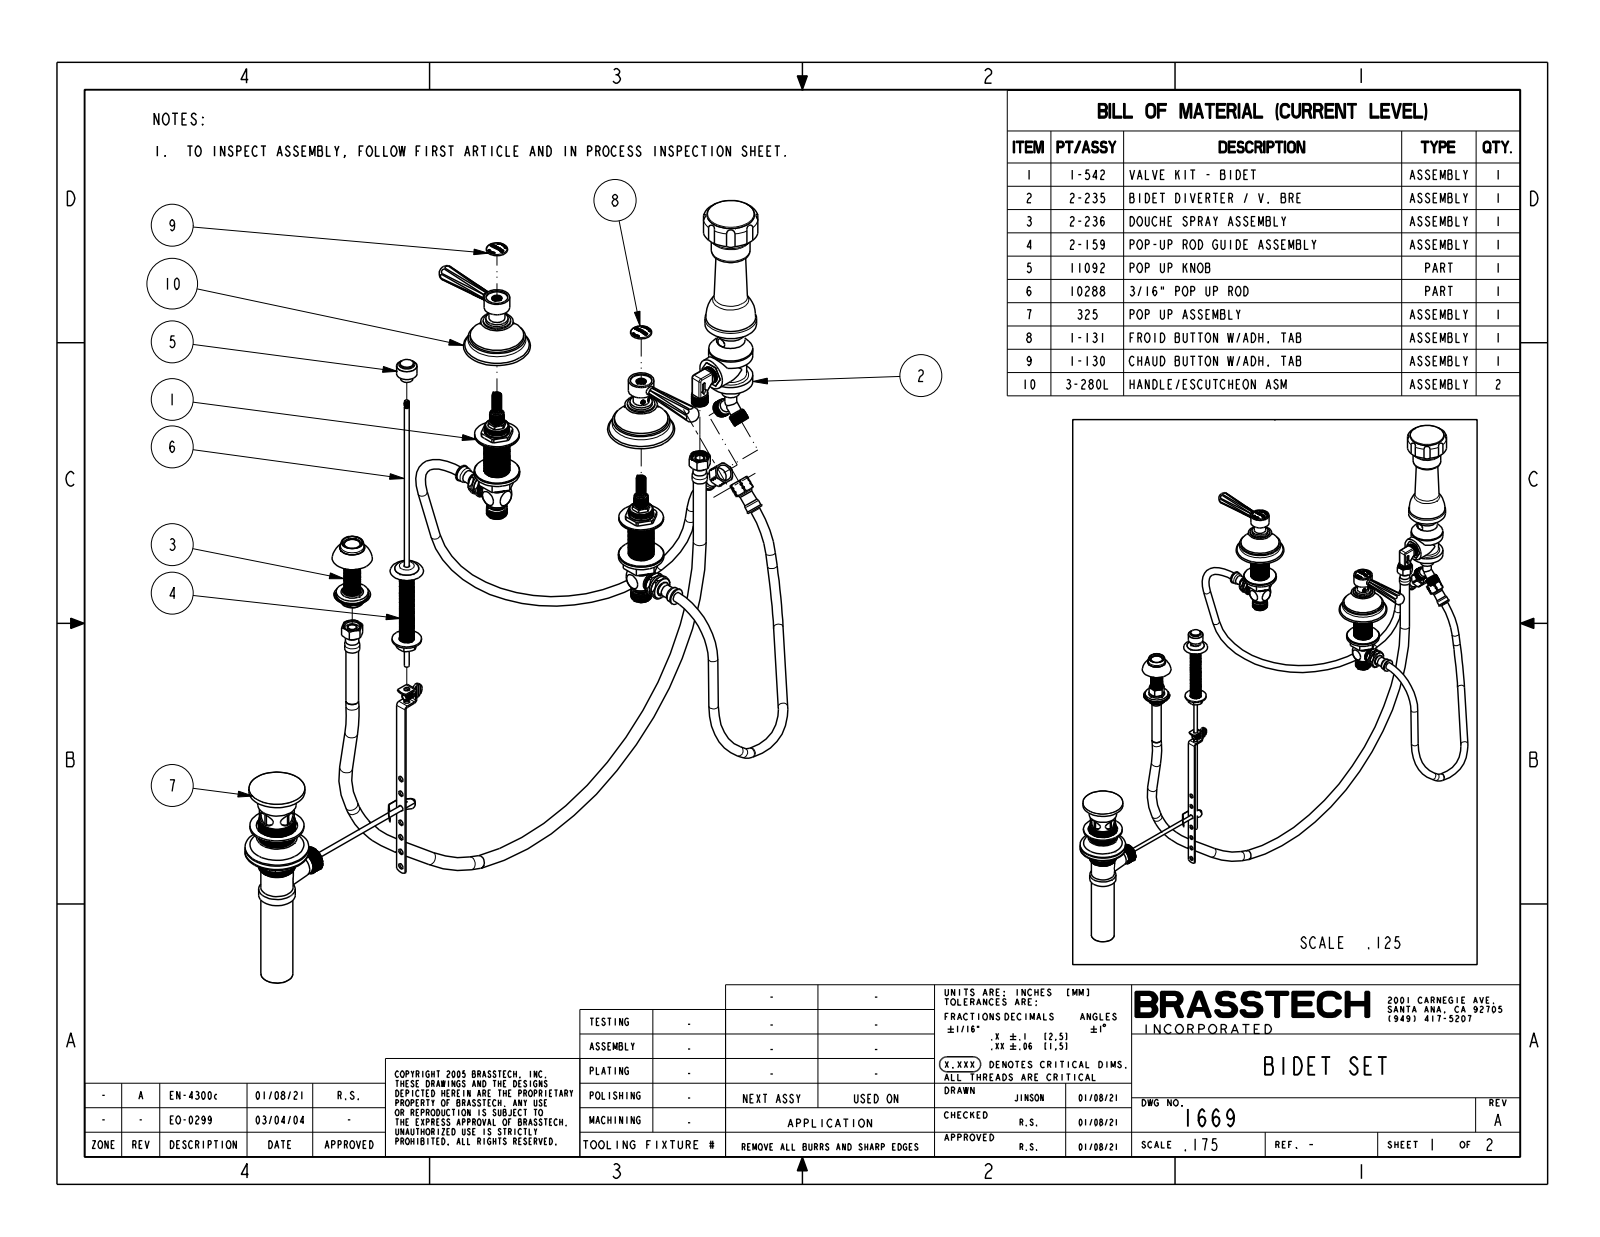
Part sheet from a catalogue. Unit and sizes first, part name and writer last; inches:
Units: inches
Overall size (bounding box): 22.856 × 14.149 × 5.353
Round holes (diameter × count): ⌀0.85 ×2, ⌀0.625 ×1, ⌀0.792 ×1, ⌀0.94 ×1
Round bosses / shafts (diameter × count): ⌀2.1 ×2, ⌀1.075 ×2, ⌀1 ×2, ⌀0.875 ×2, ⌀0.625 ×2, ⌀0.4 ×2, ⌀2.025 ×1, ⌀1.52 ×1
Partial cylindrical surfaces — rounded edges, fillets, slot ends (radius × count): R0.011 ×28, R0.025 ×17, R0.006 ×14, R0.015 ×14, R0.005 ×10, R0.014 ×9, R0.006 ×8, R0.013 ×8
Main face-to-face distances: 2.355, 0.475, 1.88, 1.375, 0.9, 0.98, 2.36, 1.885, 0.985, 0.175
Hole centre spacings: 12.647, 8
Volume: 21.92 in³ · Surface area: 99.1 in²
Bodies: 7 solids, 943 faces (449 planar, 320 cylindrical, 174 other)
Part name (STEP PRODUCT): 1669
STEP written by: CREO PARAMETRIC BY PTC INC, 2018400 (CONFIG_CONTROL_DESIGN)
